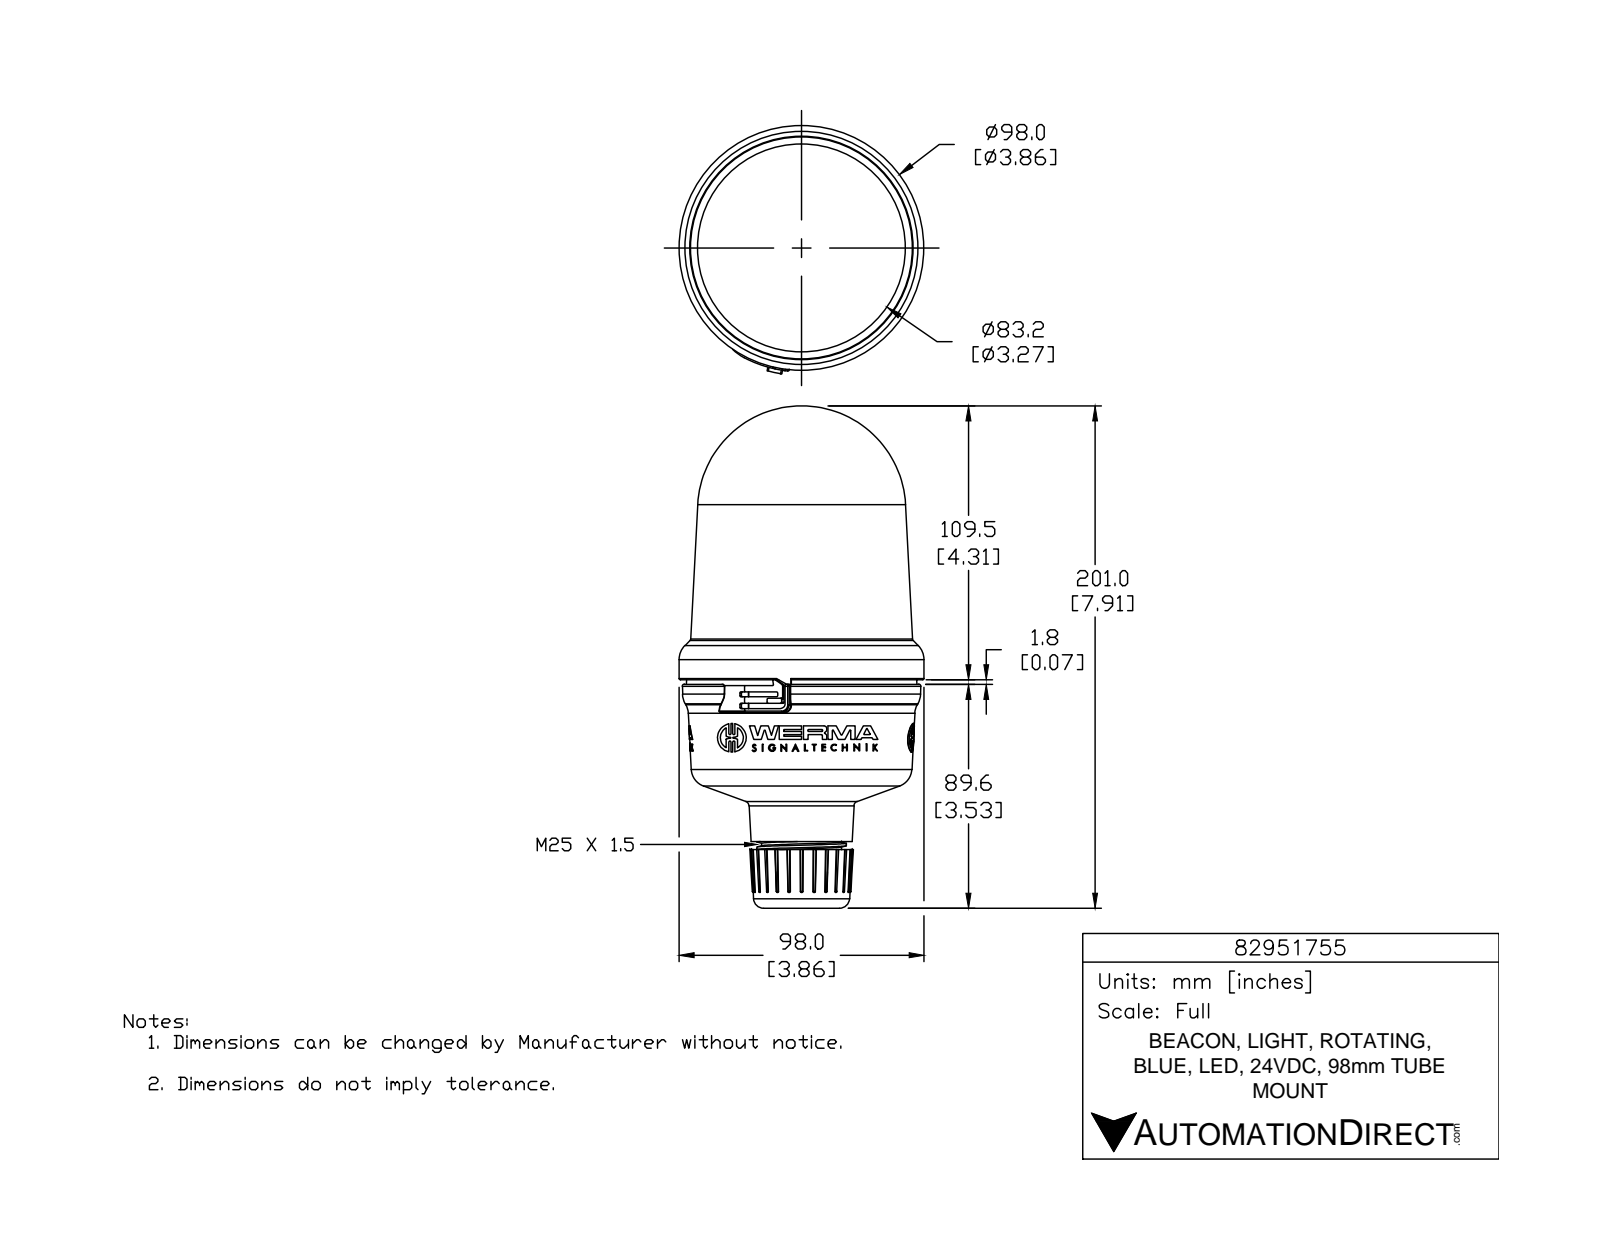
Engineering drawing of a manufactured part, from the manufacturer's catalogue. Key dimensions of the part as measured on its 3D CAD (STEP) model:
Part name (STEP PRODUCT): 82951755
STEP written by: SolidWorks 2015 (AUTOMOTIVE_DESIGN)
Units: inches
Bodies: 1 solid, 1006 faces (554 planar, 189 cylindrical, 263 other)
Overall size (bounding box): 7.914 × 3.912 × 3.858
Volume: 54.7 in³ · Surface area: 91.39 in²
Round holes (diameter × count): ⌀0.078 ×3, ⌀1.013 ×1, ⌀1.024 ×1
Round bosses / shafts (diameter × count): ⌀0.452 ×3, ⌀0.113 ×3, ⌀3.858 ×1, ⌀1.409 ×1, ⌀1.261 ×1
Partial cylindrical surfaces — rounded edges, fillets, slot ends (radius × count): R0.02 ×12, R0.007 ×9, R0.007 ×6, R0.016 ×6, R0.016 ×6, R0.016 ×6, R0.262 ×6, R0.006 ×3
Main face-to-face distances: 2.214, 0.462, 2.676, 0.335, 0.127, 2.548, 2.603, 2.476, 2.141, 0.073
